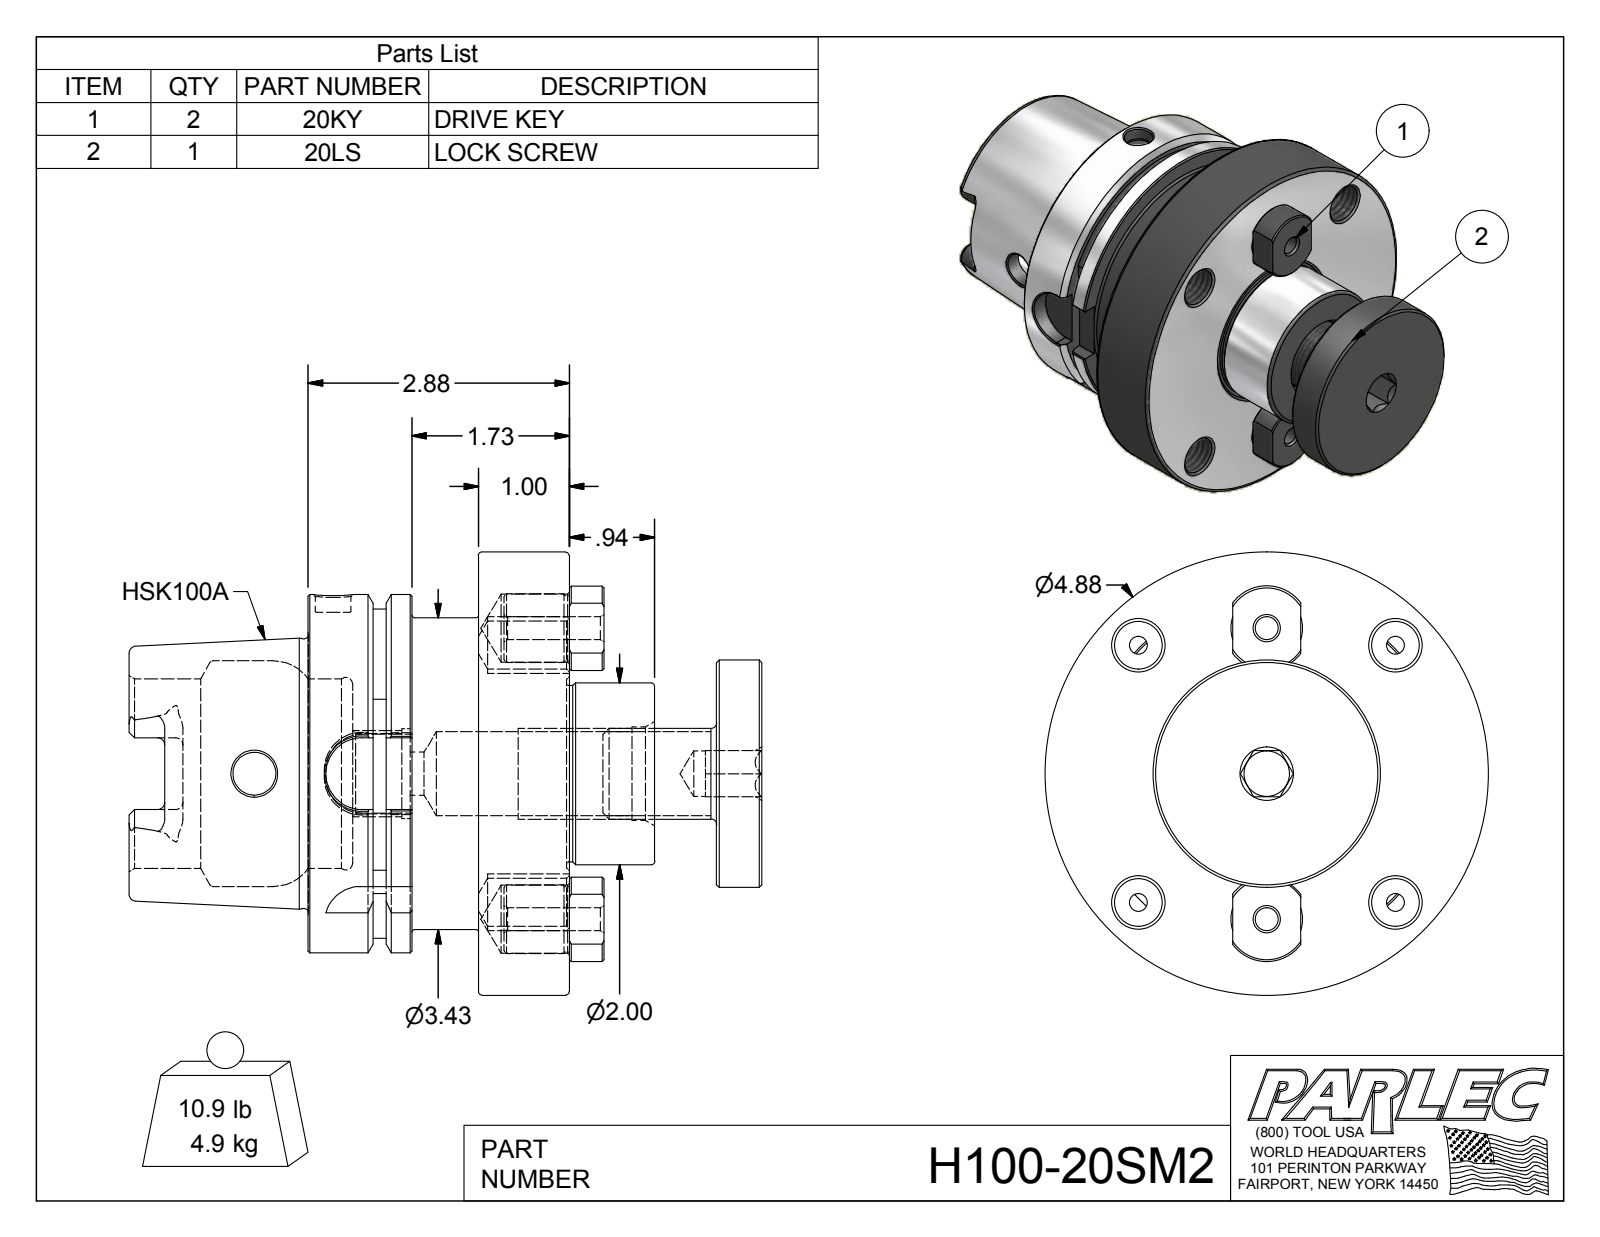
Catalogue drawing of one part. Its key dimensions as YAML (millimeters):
part_name: "H100-20SM2; 20KY; 20LS"
step_written_by: "Autodesk Inventor 2012 (AUTOMOTIVE_DESIGN)"
units: millimeters
bodies: {solids: 4, faces: 211, planar: 69, cylindrical: 56, other: 86}
overall_size: [176.8, 123.8, 123.8]
volume: 733500
surface_area: 109200
round_holes:
  - {diameter: 13.4, count: 4}
  - {diameter: 6.4, count: 2}
  - {diameter: 12, count: 2}
  - {diameter: 19.1, count: 2}
  - {diameter: 10, count: 1}
  - {diameter: 12.8, count: 1}
  - {diameter: 22.4, count: 1}
  - {diameter: 23.4, count: 1}
  - {diameter: 25, count: 1}
  - {diameter: 26.2, count: 1}
  - {diameter: 53, count: 1}
  - {diameter: 63, count: 1}
round_bosses_or_shafts:
  - {diameter: 19.2, count: 2}
  - {diameter: 18.3, count: 2}
  - {diameter: 123.8, count: 1}
  - {diameter: 100, count: 1}
  - {diameter: 87, count: 1}
  - {diameter: 75.4, count: 1}
  - {diameter: 63.5, count: 1}
  - {diameter: 50.8, count: 1}
partial_cylinders:
  - {radius: 2, count: 6}
  - {radius: 4.9, count: 4}
  - {radius: 10, count: 4}
  - {radius: 11.8, count: 2}
  - {radius: 46, count: 1}
face_to_face_distances: [25.4, 79.2, 53.8, 47.6, 73, 126.8, 114.1, 66.5, 41.1, 12.7]
hole_center_spacings: [36.2, 50.8, 71.8, 84.6, 40.6, 101.6, 81.3]
